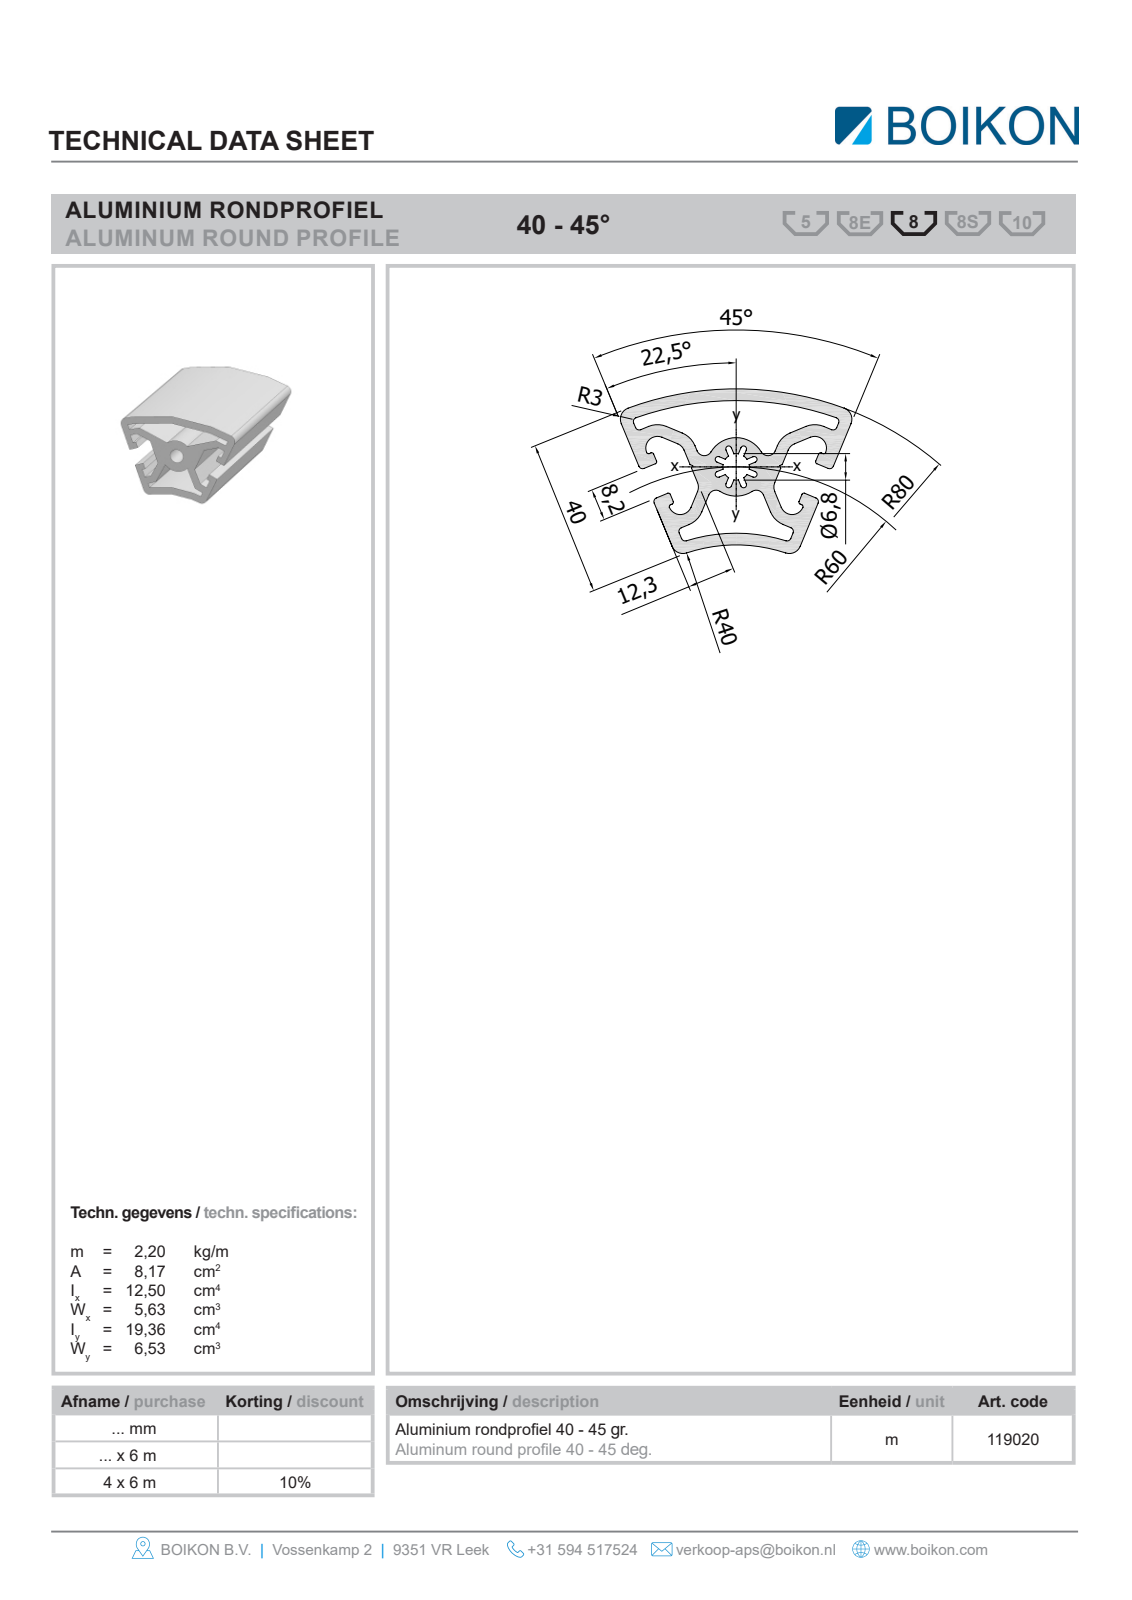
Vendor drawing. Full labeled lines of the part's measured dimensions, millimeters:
Part name (STEP PRODUCT): Root; 119020Rondprofiel 40-45gr.BOIKON0
STEP written by: HiCAD 2013 1802.4 Build 509 (AUTOMOTIVE_DESIGN)
Units: millimetres
Bodies: 1 solid, 55 faces (42 planar, 13 cylindrical, 0 other)
Overall size (bounding box): 1000 × 55.28 × 50.49
Volume: 953 503 mm³ · Surface area: 481 713 mm²
Round holes (diameter × count): ⌀6.8 ×1
Partial cylindrical surfaces — rounded edges, fillets, slot ends (radius × count): R3 ×4, R7.9 ×1, R40 ×1, R43.5 ×1, R74 ×1, R76.5 ×1, R80 ×1
Main face-to-face distances: 3.5, 12.1, 2.9, 9.2, 6.9, 7.6, 1.6, 4.5, 8.6, 1
